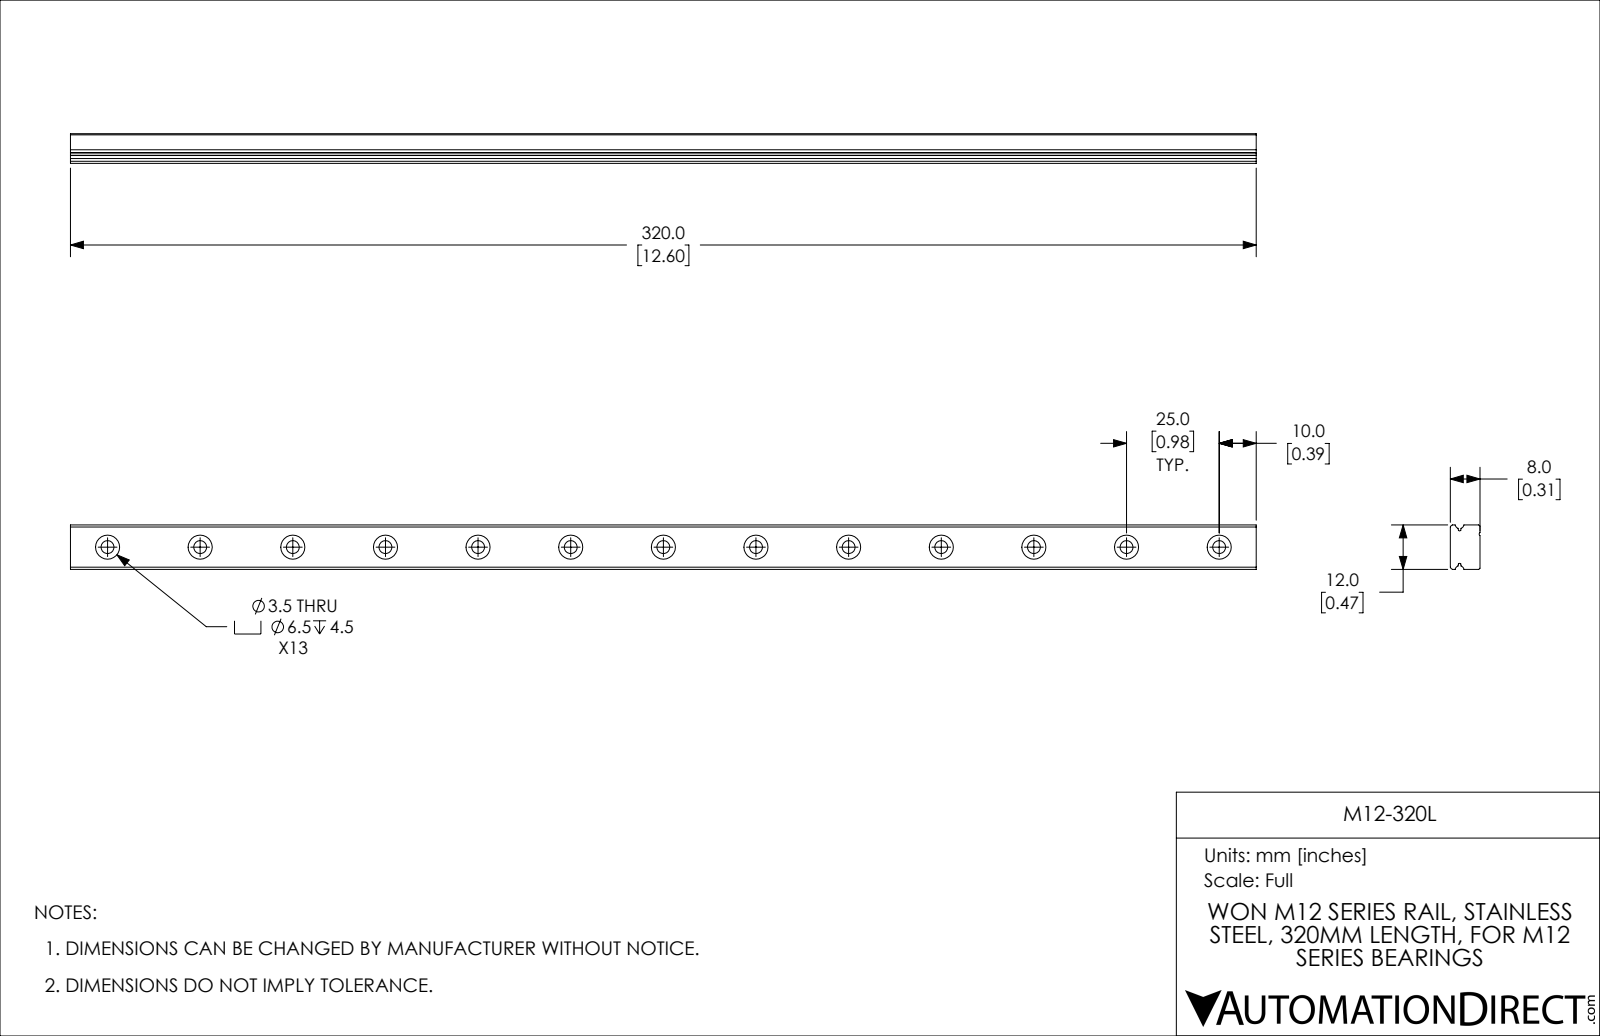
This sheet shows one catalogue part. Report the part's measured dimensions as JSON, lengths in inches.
{"part_name": "M12-320L", "step_written_by": "SolidWorks 2019 (CONFIG_CONTROL_DESIGN)", "units": "inches", "bodies": {"solids": 1, "faces": 90, "planar": 26, "cylindrical": 64, "other": 0}, "overall_size": [12.598, 0.472, 0.315], "volume_in3": 1.636, "surface_area_in2": 23.92, "round_holes": [[0.138, 13], [0.256, 13]], "partial_cylinders_radius": [[0.017, 2], [0.039, 2], [0.045, 2], [0.047, 2], [0.02, 1]], "face_to_face_distances": [0.315, 0.472, 0.023, 0.138, 0.177, 12.598], "hole_center_spacings": [0.984, 1.969, 2.953, 3.937, 4.921, 5.906, 6.89, 7.874]}
